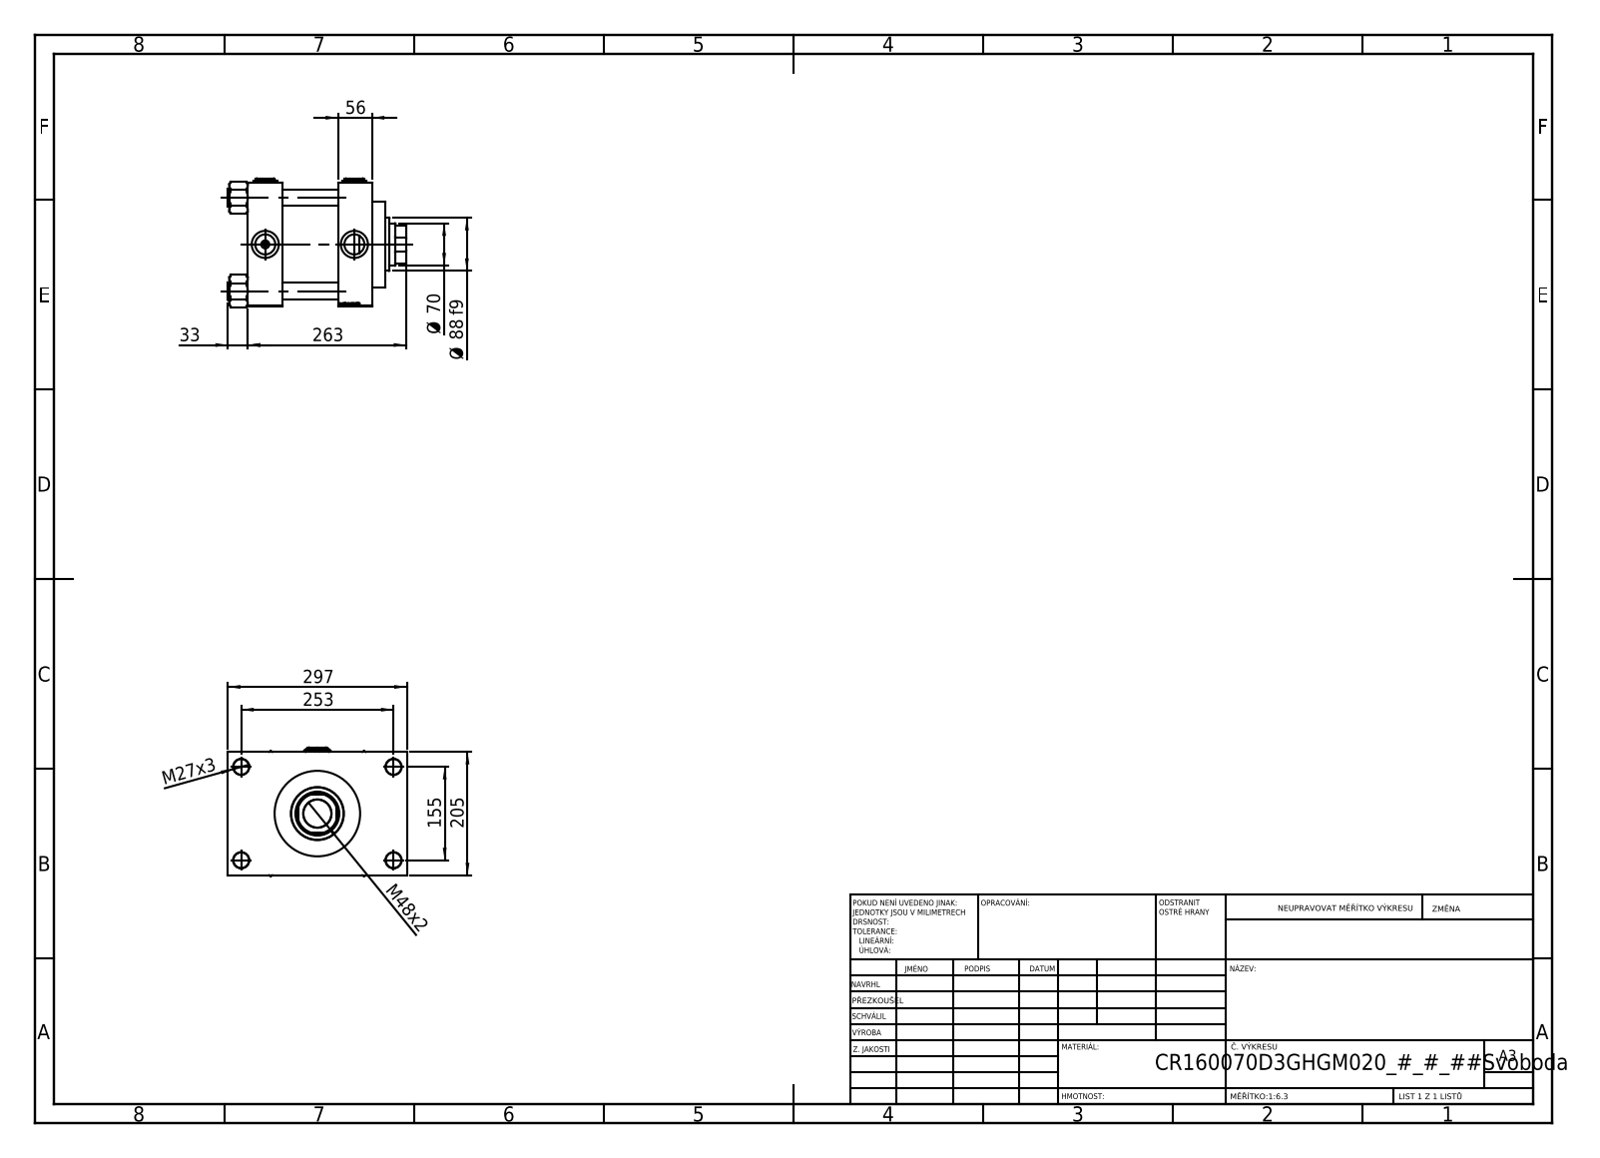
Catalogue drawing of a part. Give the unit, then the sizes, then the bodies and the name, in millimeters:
Units: millimetres
Overall size (bounding box): 297 × 296 × 213.57
Round holes (diameter × count): ⌀26 ×4, ⌀27 ×4, ⌀33.24 ×4, ⌀45 ×4, ⌀7 ×3, ⌀46.5 ×1, ⌀70 ×1, ⌀73 ×1, ⌀120 ×1, ⌀142 ×1, ⌀160 ×1
Round bosses / shafts (diameter × count): ⌀30 ×4, ⌀166 ×1, ⌀88 ×1
Partial cylindrical surfaces — rounded edges, fillets, slot ends (radius × count): R34 ×1
Main face-to-face distances: 58, 150, 92, 148, 206, 56, 205, 46, 251, 72
Hole centre spacings: 49.05, 109.53, 148.35, 154.9, 162.53, 203.95, 256.13, 148
Volume: 7 823 000 mm³ · Surface area: 741 550 mm²
Bodies: 13 solids, 1249 faces (592 planar, 97 cylindrical, 560 other)
Part name (STEP PRODUCT): V215_VC_A; NUT_M5_D; V215CR_D_Body; V215CR_VCP_D (+2 more)
STEP written by: SolidWorks 2019 (CONFIG_CONTROL_DESIGN)
